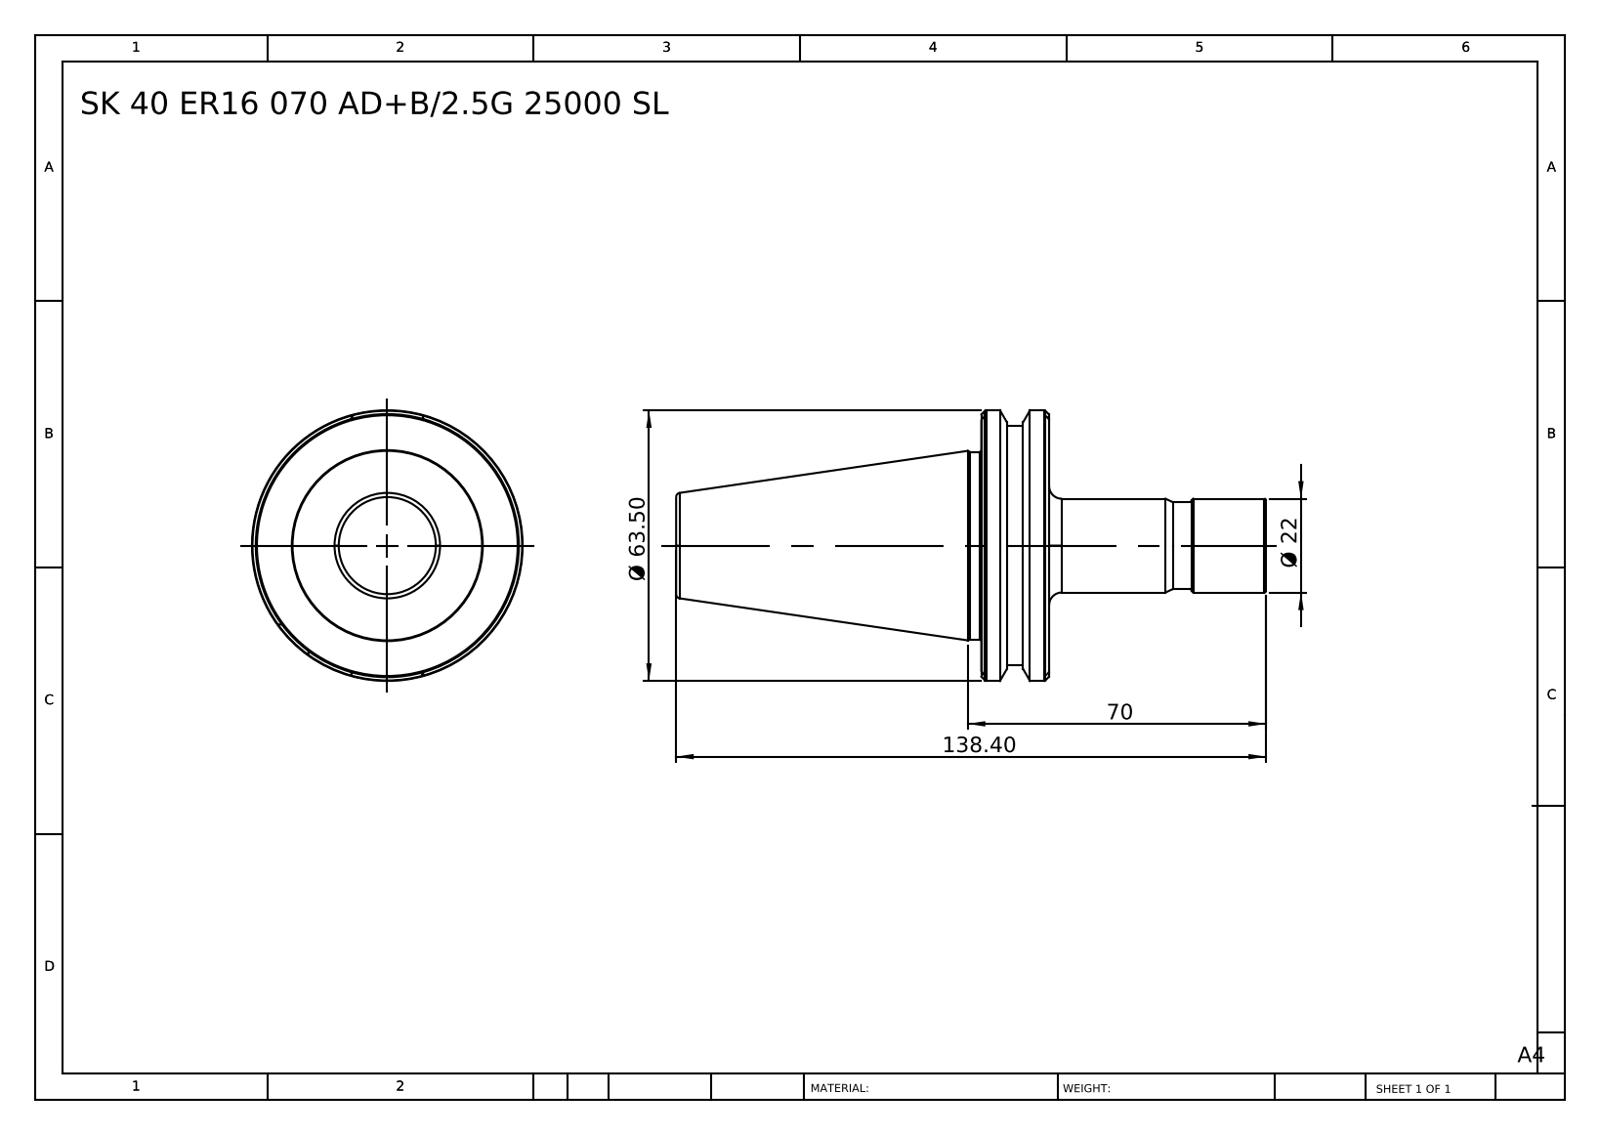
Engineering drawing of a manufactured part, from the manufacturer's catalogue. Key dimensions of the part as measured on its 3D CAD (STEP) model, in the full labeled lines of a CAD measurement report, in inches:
Part name (STEP PRODUCT): SK40 ER16M 070 AD+B 2.5G 25000 SL
STEP written by: SolidWorks 2014 (CONFIG_CONTROL_DESIGN)
Units: inches
Bodies: 1 solid, 82 faces (7 planar, 14 cylindrical, 61 other)
Overall size (bounding box): 5.449 × 2.5 × 2.5
Volume: 8.317 in³ · Surface area: 31.58 in²
Round bosses / shafts (diameter × count): ⌀2.5 ×1, ⌀2.205 ×1, ⌀1.732 ×1, ⌀0.866 ×1, ⌀0.803 ×1
Main face-to-face distances: 0.626, 3.445, 2.819, 2.004, 2.63, 5.449, 2.394, 0.39, 0.236, 3.055
